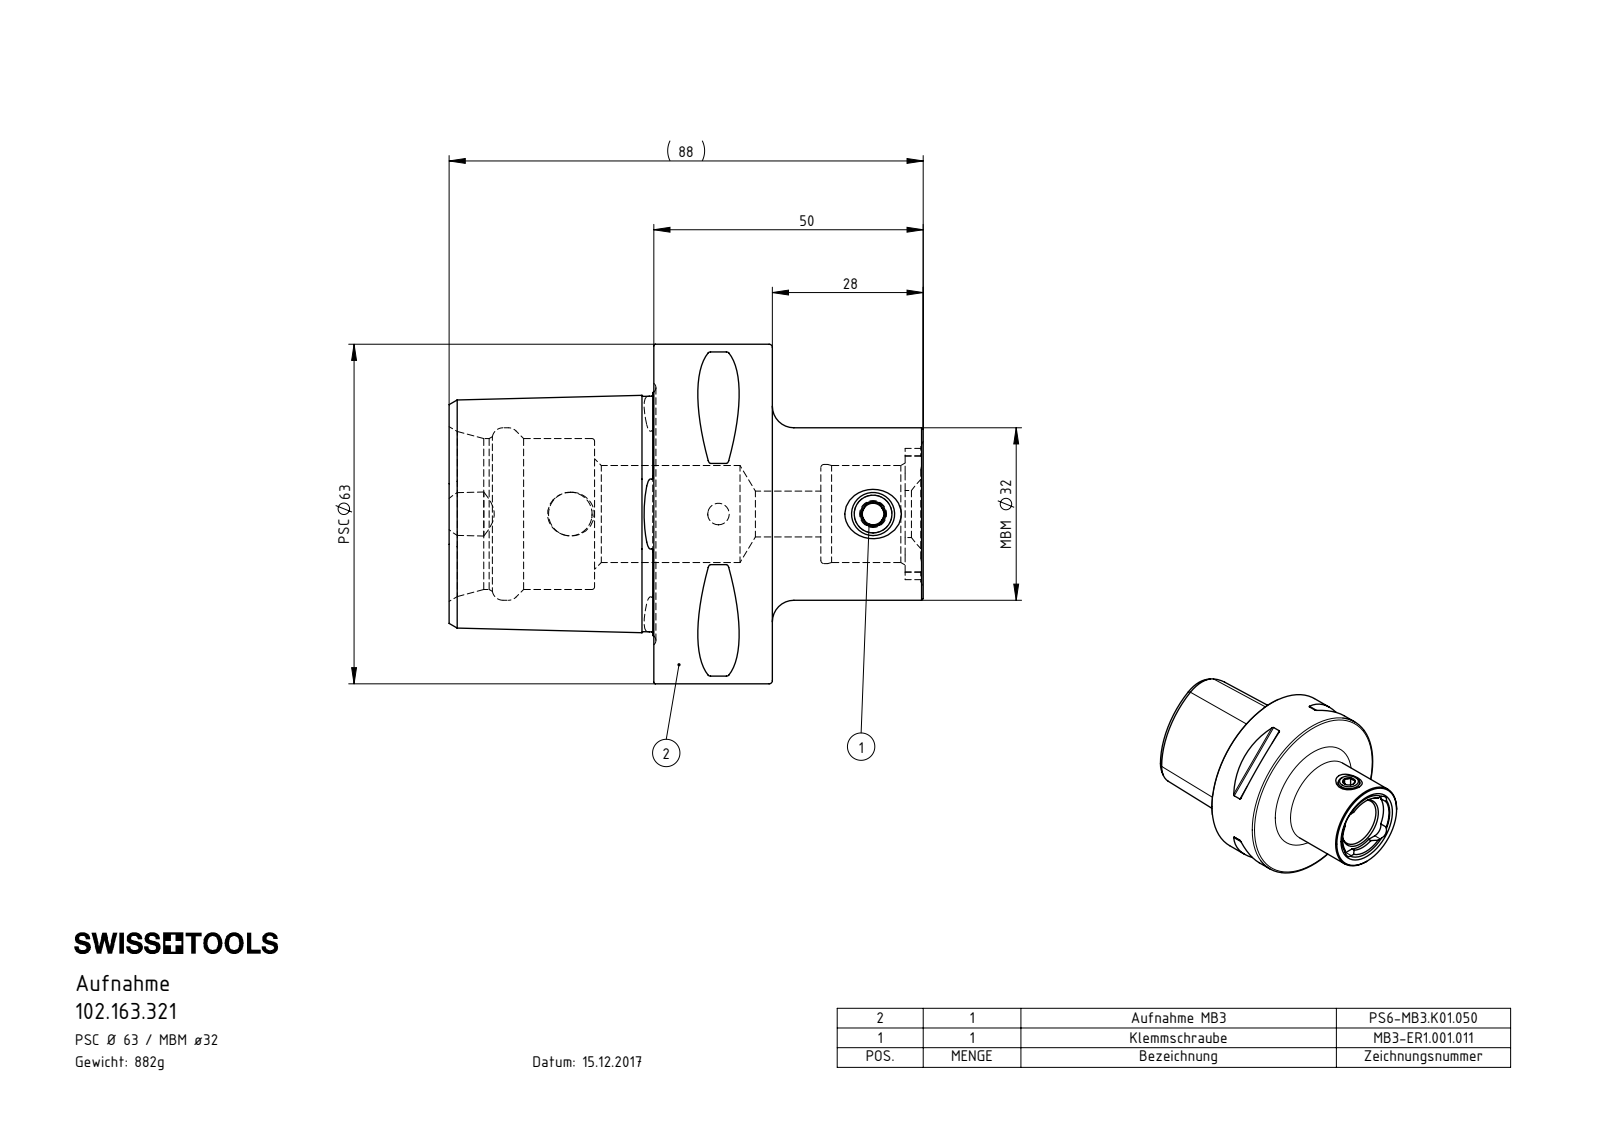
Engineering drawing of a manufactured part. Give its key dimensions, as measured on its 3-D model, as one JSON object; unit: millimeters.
{"part_name": "102.163.321; PS6-MB3.K01.050_B; MB3-ER1.001.011_A", "step_written_by": "SolidWorks 2022 (CONFIG_CONTROL_DESIGN)", "units": "millimeters", "bodies": {"solids": 2, "faces": 197, "planar": 44, "cylindrical": 50, "other": 103}, "overall_size": [88, 63, 63], "volume_mm3": 112340, "surface_area_mm2": 24322, "round_holes": [[4, 2], [7, 1], [8.1, 1], [8.5, 1], [18, 1], [18.4, 1], [28, 1], [32, 1]], "round_bosses_or_shafts": [[63, 1], [8, 1]], "partial_cylinders_radius": [[0.5, 8], [3.2, 4], [6, 1], [10.5, 1], [12.18, 1]], "face_to_face_distances": [22, 38, 60, 24.88, 27, 11, 33, 88, 61, 50], "hole_center_spacings": [27.5, 28.7, 56.2]}
